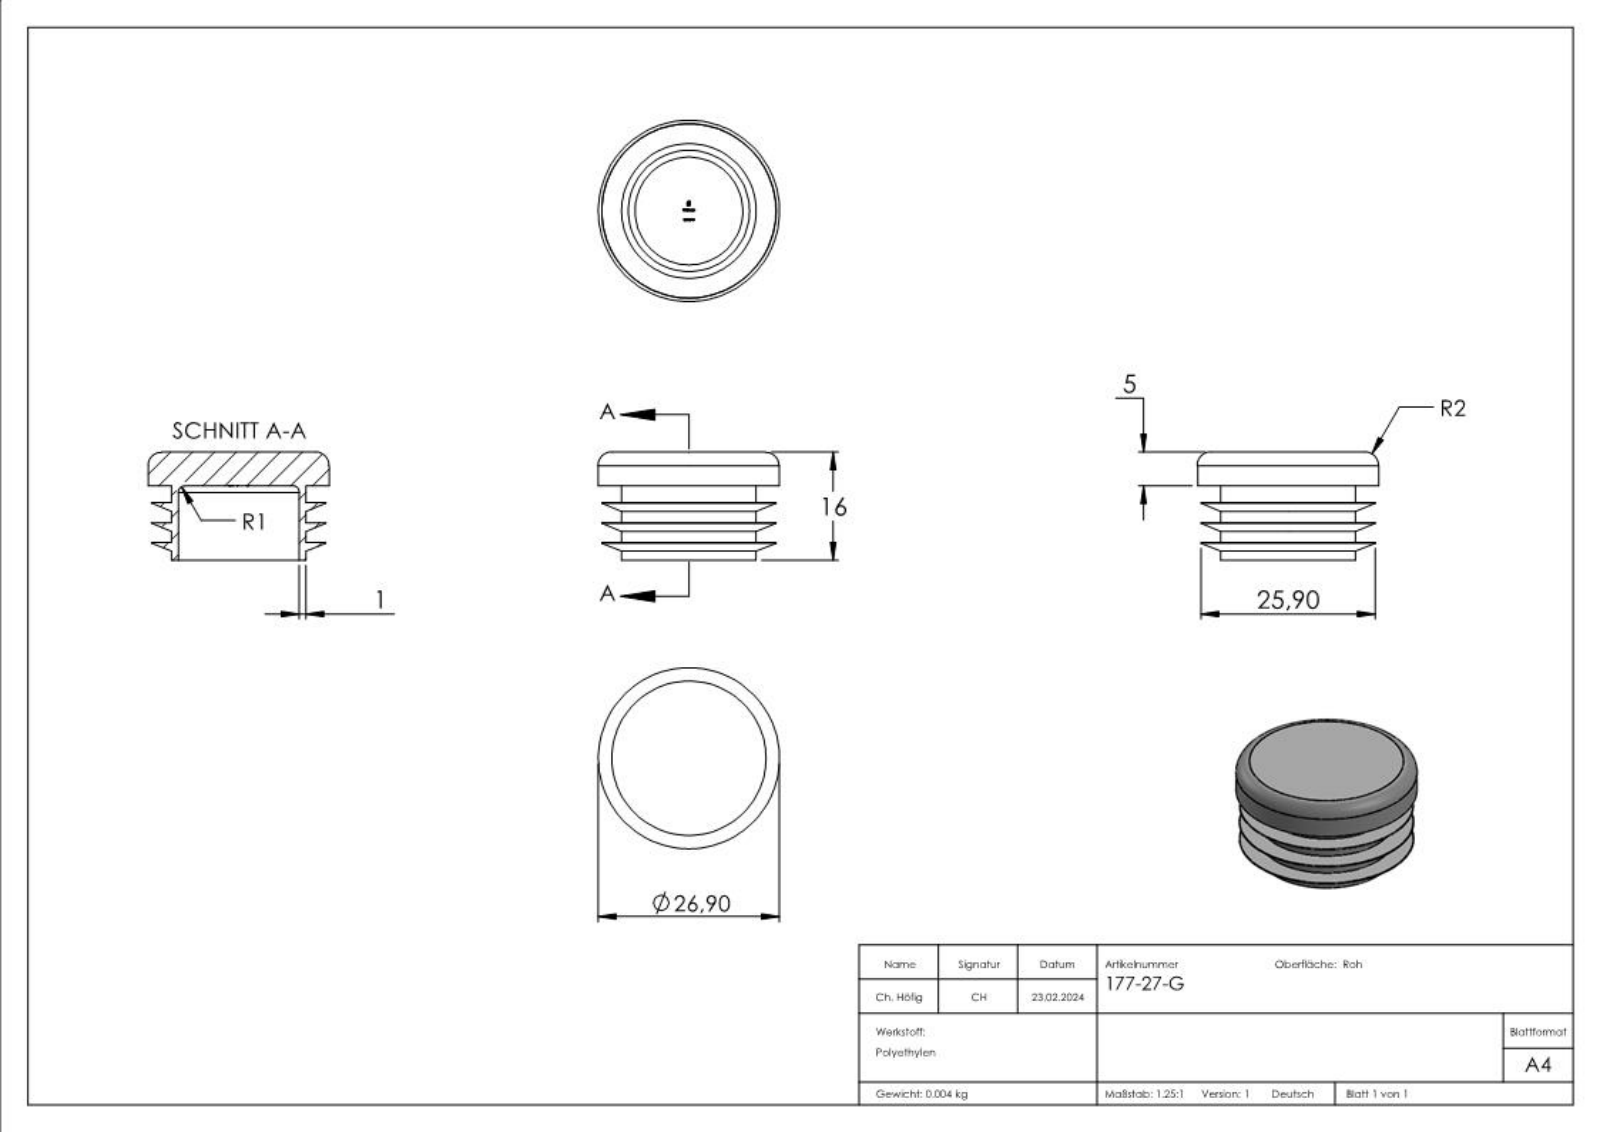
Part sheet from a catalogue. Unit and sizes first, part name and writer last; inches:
Units: inches
Overall size (bounding box): 1.059 × 1.059 × 0.63
Round holes (diameter × count): ⌀0.709 ×1
Round bosses / shafts (diameter × count): ⌀1.059 ×1, ⌀0.787 ×1
Main face-to-face distances: 0.116, 0.197, 0.215, 0.411, 0.331, 0.528, 0.232, 0.098, 0.295, 0.102
Volume: 0.236 in³ · Surface area: 6.002 in²
Bodies: 1 solid, 240 faces (143 planar, 6 cylindrical, 91 other)
Part name (STEP PRODUCT): 177-27-G
STEP written by: SolidWorks 2018 (CONFIG_CONTROL_DESIGN)
